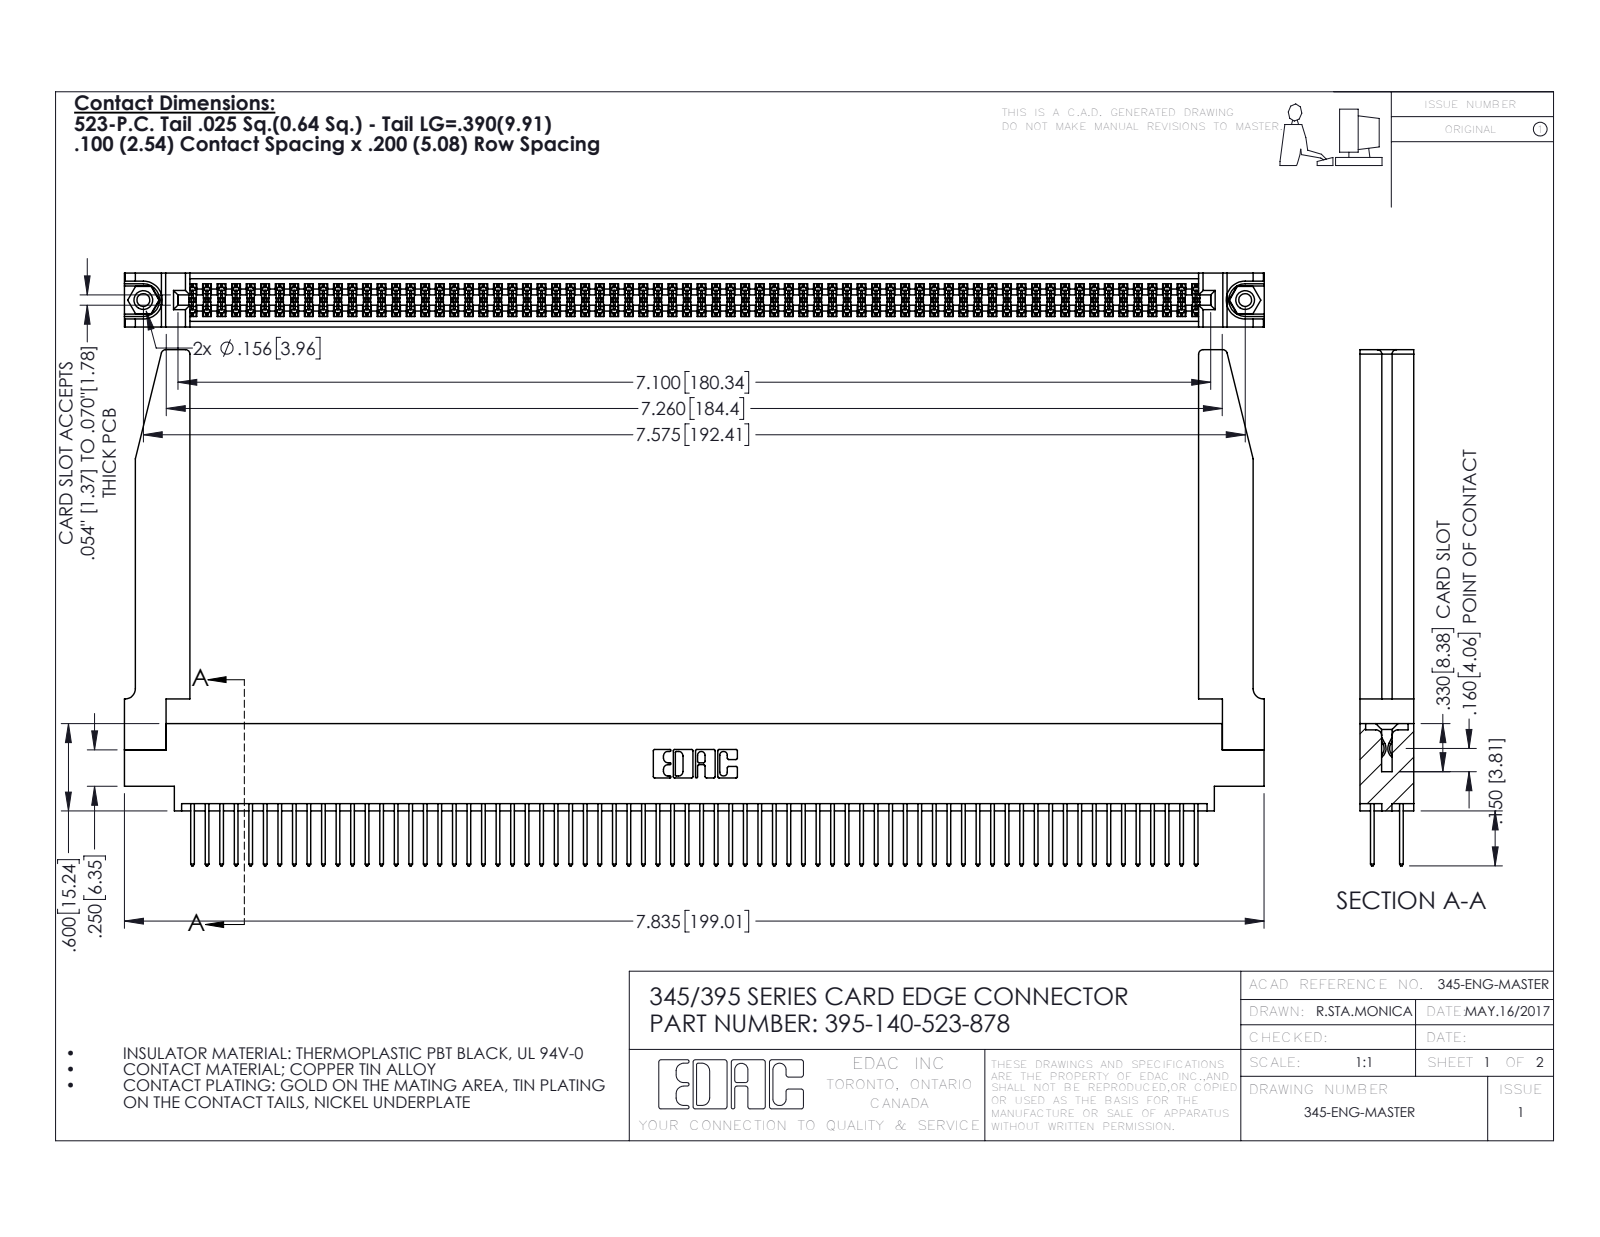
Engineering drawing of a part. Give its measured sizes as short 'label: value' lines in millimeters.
name: 395-140-523-878; 345-292-001_345-293-123; 345-220-078_345-220-078; 345-250-001_345-250-001-102 (+1 more)
written by: SolidWorks 2016 (CONFIG_CONTROL_DESIGN)
unit: mm
bodies: 145 solids, 7364 faces (4846 planar, 2466 cylindrical, 52 other)
size: 199 × 90.1 × 9.4
volume: 27 530 mm³; area: 38 030 mm²
holes: 2× ⌀2.3, 2× ⌀3.2, 2× ⌀4, 1× ⌀1.6
bosses: 2× ⌀3.9
rounds: 210× R0.2, 140× R0.3, 22× R0.3, 8× R0.8, 6× R0.2, 6× R0.8, 3× R0.7, 2× R0.4
face distances: 1.8, 7.6, 9.4, 2.5, 6.9, 0.6, 5.1, 5.7, 4.4, 3.8
hole spacings: 6.9, 186.4, 192.4
